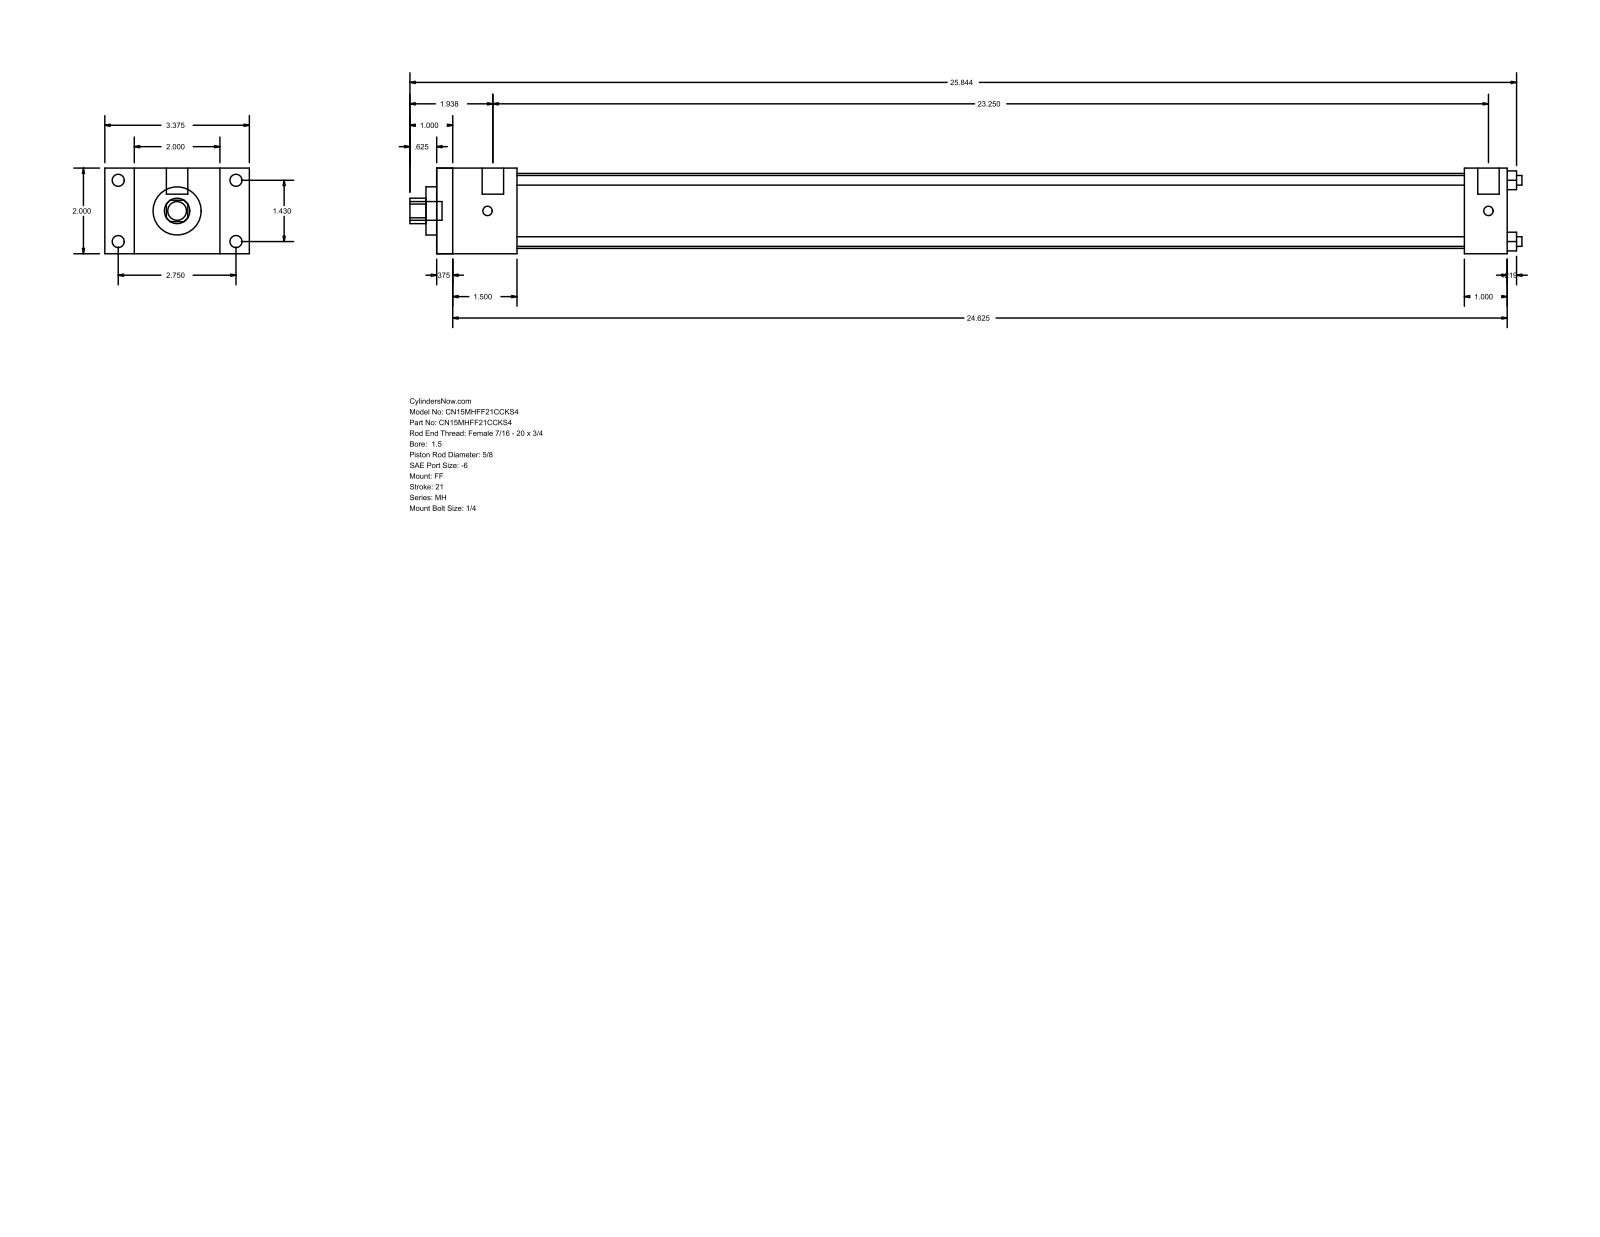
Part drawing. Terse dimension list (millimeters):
name: MH_FF__0150_0.625
written by: GSSL Pune (CONFIG_CONTROL_DESIGN)
unit: mm
bodies: 0 solids, 92 faces (64 planar, 28 cylindrical, 0 other)
size: 659.61 × 85.72 × 50.8
holes: 4× ⌀5.71, 1× ⌀15.88, 1× ⌀28.57, 1× ⌀44.45
bosses: 4× ⌀7.14, 4× ⌀5.56, 2× ⌀12.7, 1× ⌀11.11
rounds: 1× R7.54
face distances: 50.8, 635, 9.52, 625.48, 25.4, 17.46, 68.26, 47.62, 38.1, 587.38
hole spacings: 25.68, 36.32, 51.36
